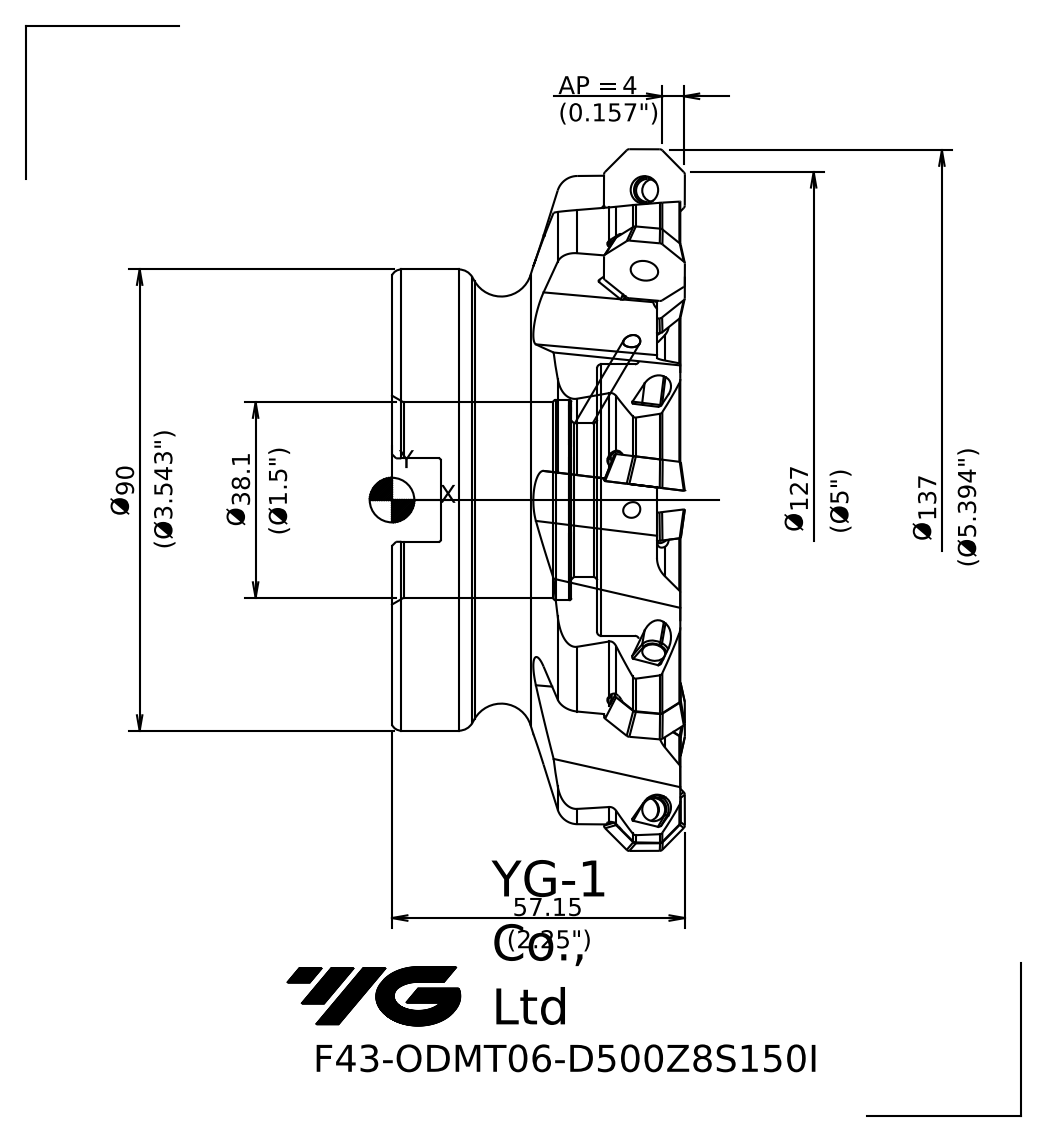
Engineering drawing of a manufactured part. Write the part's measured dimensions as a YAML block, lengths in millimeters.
part_name: "102230FC773B3alp"
step_written_by: "SIEMENS PLM Software NX 10.0 (AP203_CONFIGURATION_CONTROLLED_3D_DESIGN_OF_MECHANICAL_PARTS_AND_ASSEMBLIES_MIM_LF)"
units: millimeters
bodies: {solids: 1, faces: 70, planar: 16, cylindrical: 11, other: 43}
overall_size: [137.08, 137.08, 57.15]
volume: 393917
surface_area: 69842
round_holes:
  - {diameter: 30, count: 1}
  - {diameter: 38.1, count: 1}
  - {diameter: 39.1, count: 1}
  - {diameter: 53, count: 1}
round_bosses_or_shafts:
  - {diameter: 134.69, count: 1}
  - {diameter: 126.86, count: 1}
  - {diameter: 90, count: 1}
partial_cylinders:
  - {radius: 0.4, count: 2}
face_to_face_distances: [51.71, 11.71, 40, 42.18, 30.47, 9.53, 16.28, 16.71, 5, 25.47]
